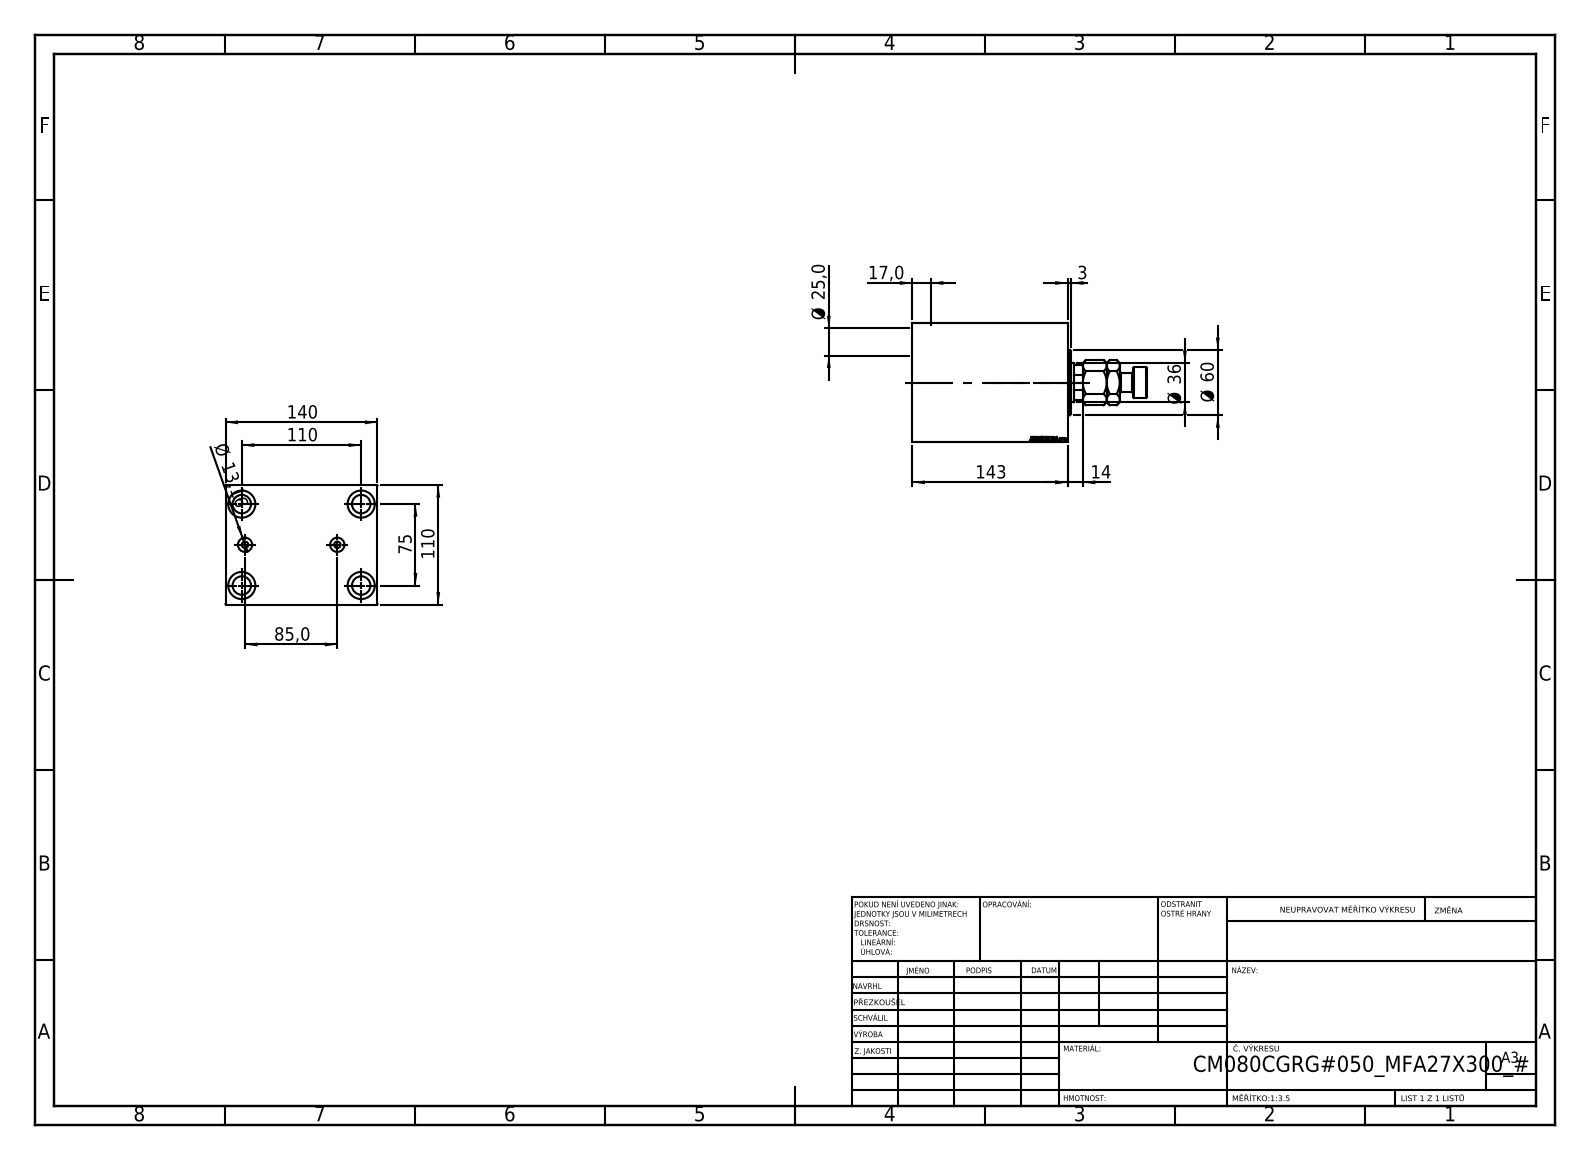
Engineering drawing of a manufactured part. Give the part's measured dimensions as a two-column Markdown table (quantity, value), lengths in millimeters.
| quantity | value |
| --- | --- |
| part name | V450CM_C_Body; V450CM_VC_B; MFA; V450CM_C_VCP |
| STEP written by | SolidWorks 2019 (CONFIG_CONTROL_DESIGN) |
| units | millimeters |
| bodies | 4 solids, 912 faces (424 planar, 62 cylindrical, 426 other) |
| overall size | 216 × 140 × 110 |
| volume | 1 879 000 mm³ |
| surface area | 229 226 mm² |
| round holes (diameter × count) | 17 × 4, 25 × 4, 6 × 2, 13.16 × 2, 25.5 × 1, 36 × 1, 39.5 × 1, 80 × 1, 82 × 1, 87 × 1 |
| round bosses / shafts (diameter × count) | 60 × 1, 28 × 1, 18 × 1 |
| partial cylindrical surfaces (radius × count) | 17.5 × 1 |
| main face-to-face distances | 110, 140, 143, 122, 21, 14, 129, 108, 64, 50 |
| hole center spacings | 66.57, 37.62, 43.48, 75, 95.66, 110, 113.38, 133.14 |
